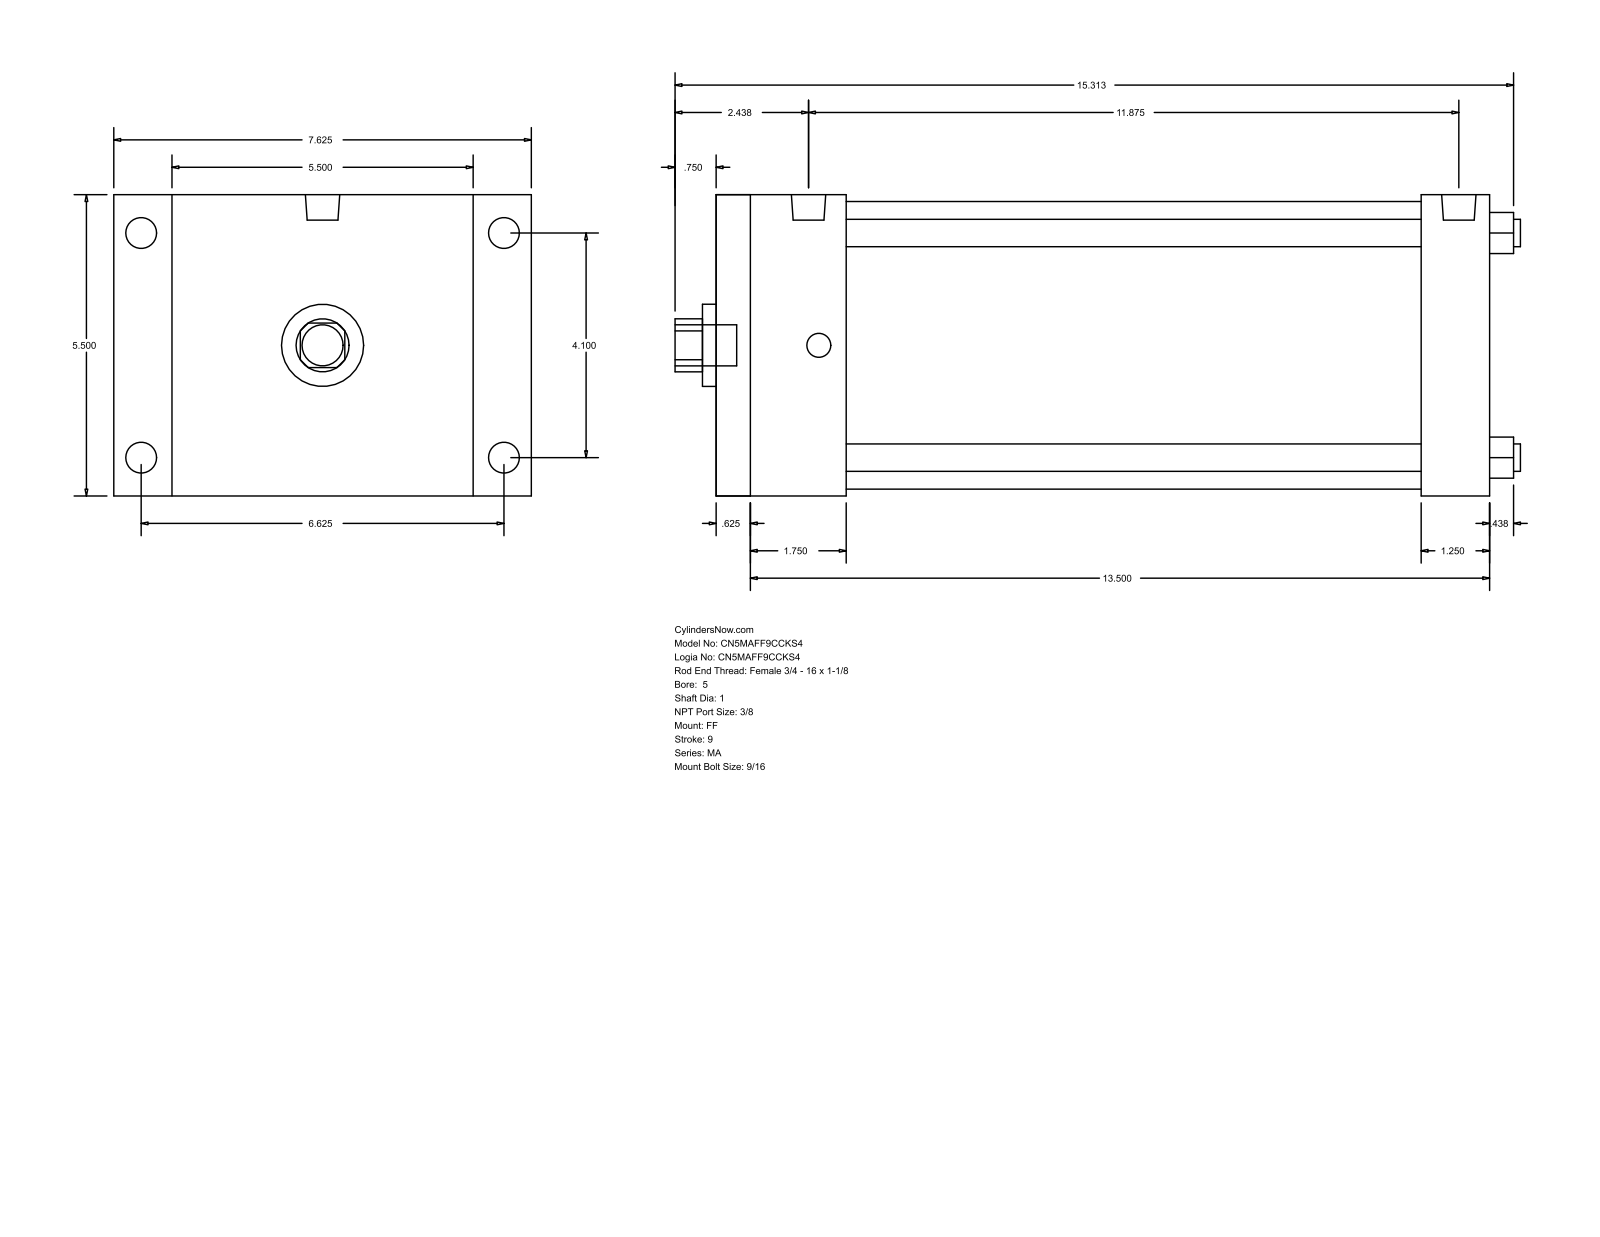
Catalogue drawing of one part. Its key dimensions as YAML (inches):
part_name: "MA_FF__0500_1"
step_written_by: "GSSL Pune (CONFIG_CONTROL_DESIGN)"
units: inches
bodies: {solids: 0, faces: 92, planar: 64, cylindrical: 28, other: 0}
overall_size: [15.437, 7.625, 5.5]
round_holes:
  - {diameter: 0.5, count: 4}
  - {diameter: 1, count: 1}
  - {diameter: 1.5, count: 1}
  - {diameter: 5.25, count: 1}
round_bosses_or_shafts:
  - {diameter: 0.563, count: 4}
  - {diameter: 0.437, count: 4}
  - {diameter: 0.627, count: 2}
  - {diameter: 0.75, count: 1}
partial_cylinders:
  - {radius: 0.484, count: 1}
face_to_face_distances: [5.5, 14.125, 0.625, 13.5, 12.875, 12.25, 1.25, 2.375, 1.75, 10.5]
hole_center_spacings: [2.899, 4.1, 5.798]
